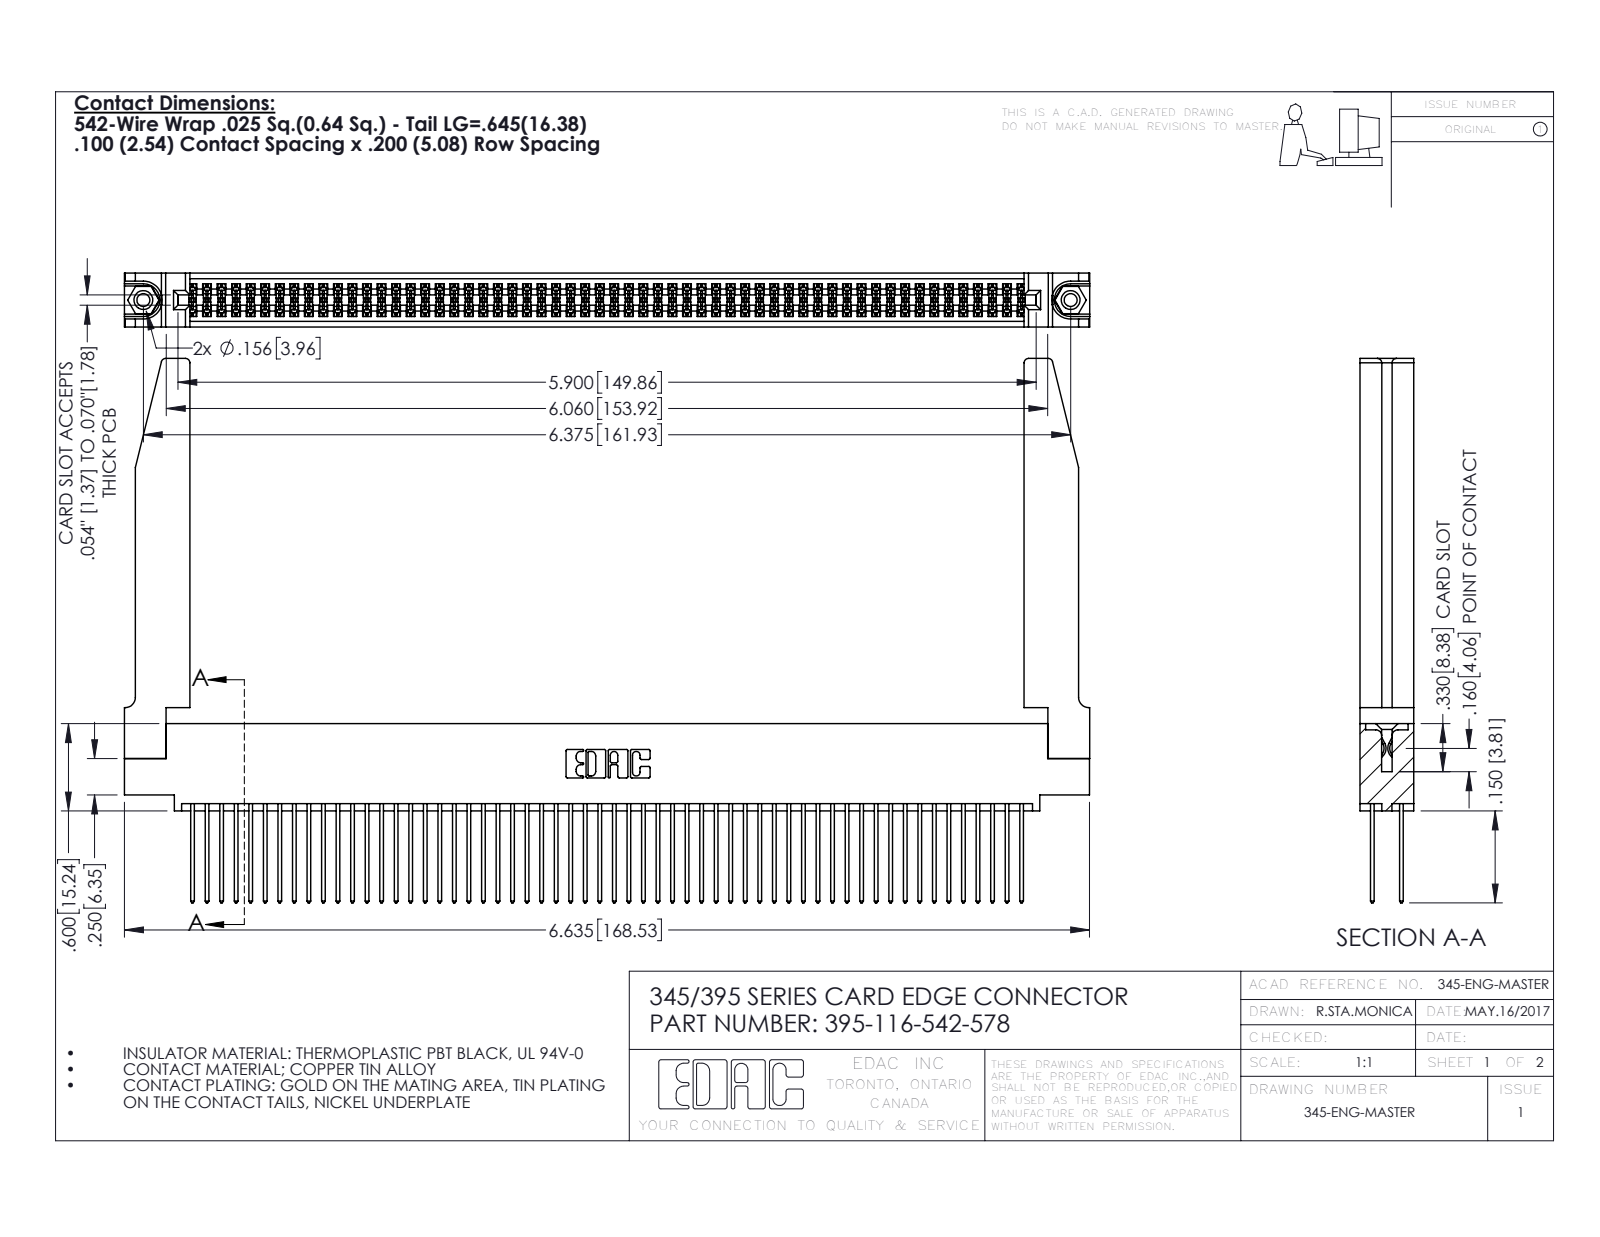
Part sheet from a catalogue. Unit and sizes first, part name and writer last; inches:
Units: inches
Overall size (bounding box): 6.636 × 3.742 × 0.37
Round holes (diameter × count): ⌀0.089 ×2, ⌀0.125 ×2, ⌀0.156 ×2, ⌀0.064 ×1
Round bosses / shafts (diameter × count): ⌀0.155 ×2
Partial cylindrical surfaces — rounded edges, fillets, slot ends (radius × count): R0.006 ×174, R0.01 ×116, R0.01 ×22, R0.03 ×8, R0.007 ×6, R0.031 ×6, R0.026 ×3, R0.014 ×2
Main face-to-face distances: 0.072, 0.298, 0.37, 0.2, 0.098, 0.272, 0.025, 0.225, 0.175, 0.15
Hole centre spacings: 0.27, 6.139, 6.375
Volume: 1.511 in³ · Surface area: 54.07 in²
Bodies: 121 solids, 6164 faces (4054 planar, 2058 cylindrical, 52 other)
Part name (STEP PRODUCT): 345-220-078_345-220-078; 395-116-542-578; 345-250-001_345-250-001-102; 345 Part_0.110 Offset - 0.156 Dia-TH (+1 more)
STEP written by: SolidWorks 2016 (CONFIG_CONTROL_DESIGN)
